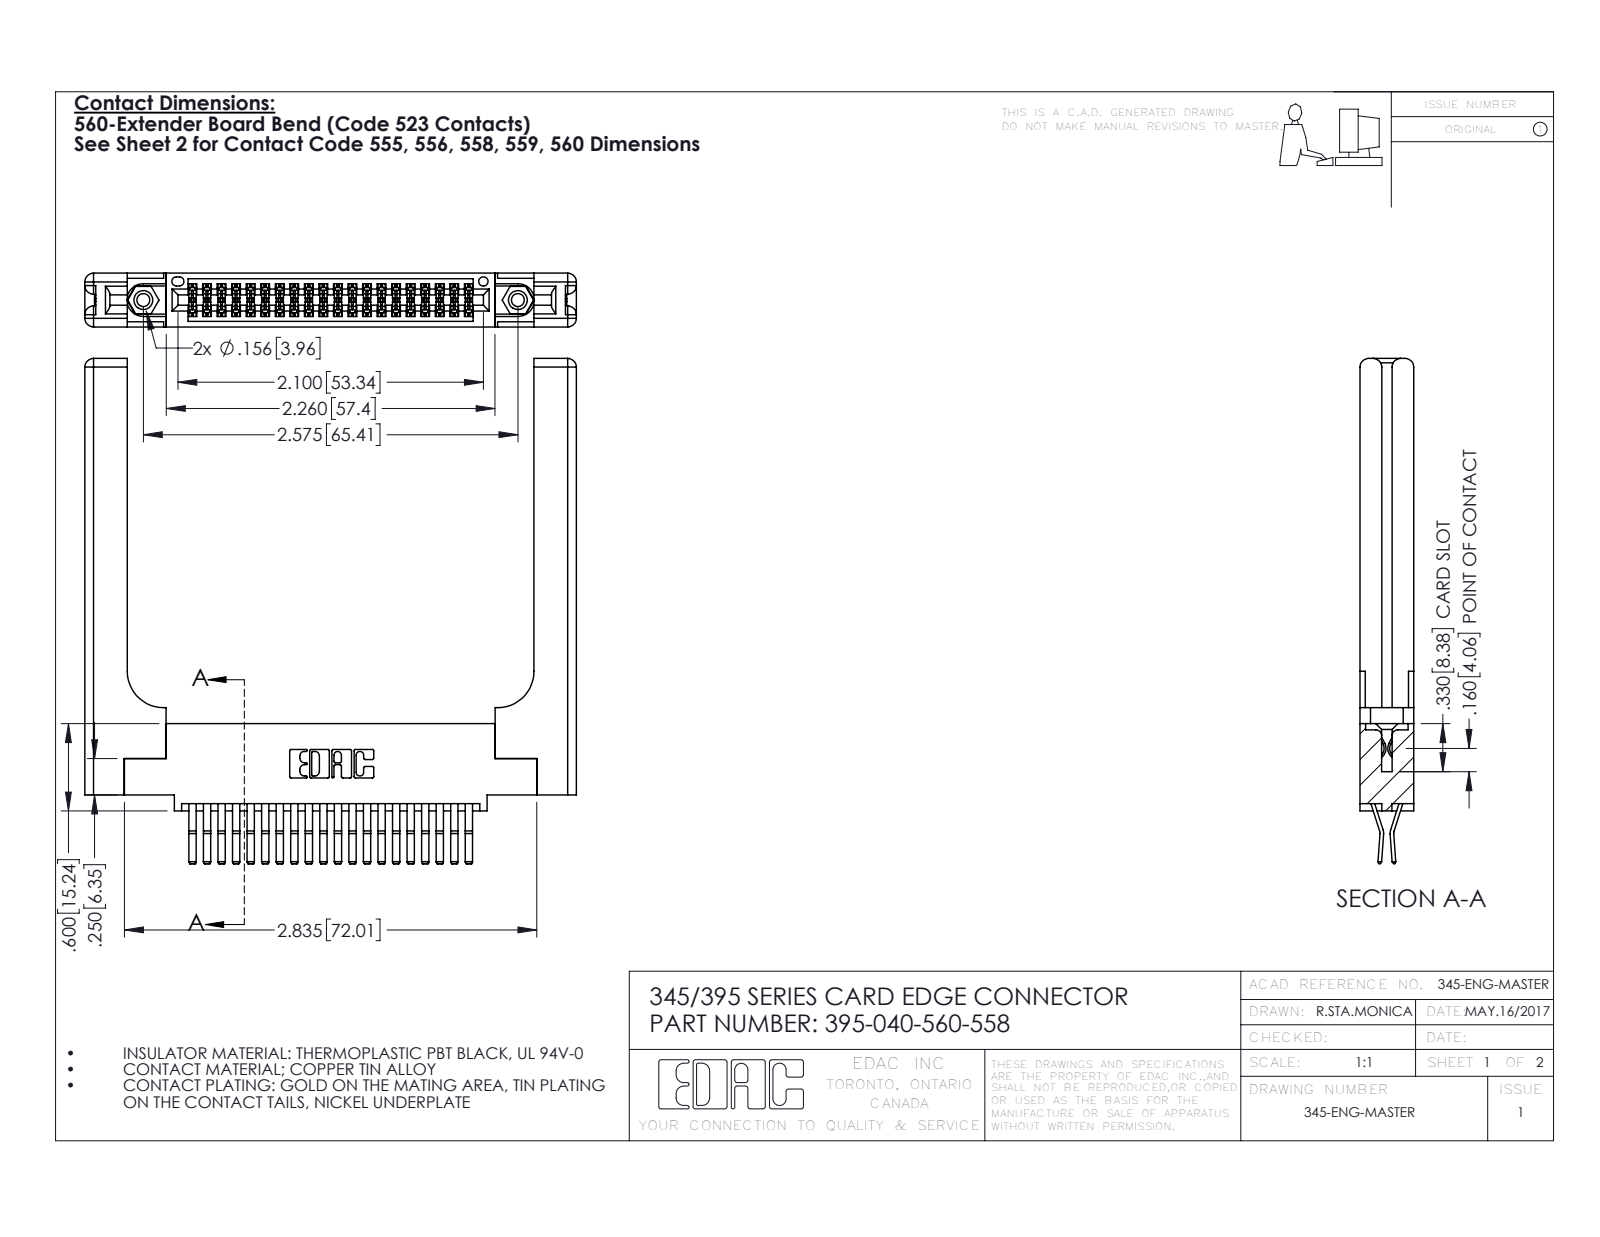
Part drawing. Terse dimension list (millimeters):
name: 395-040-560-558; 345-250-001_345-250-001-102; 345-292-001_560 Tail; 345 Part_0.110 Offset - 0.156 Dia-TH (+1 more)
written by: SolidWorks 2016 (CONFIG_CONTROL_DESIGN)
unit: mm
bodies: 45 solids, 2466 faces (1552 planar, 854 cylindrical, 60 other)
size: 88.2 × 85.8 × 9.4
volume: 16 800 mm³; area: 17 700 mm²
holes: 2× ⌀2.3, 2× ⌀3.2, 2× ⌀4, 1× ⌀1.6
bosses: 2× ⌀3.9
rounds: 60× R0.2, 22× R0.3, 16× R1.5, 6× R0.2, 6× R0.8, 3× R0.7, 2× R0.3, 2× R0.4
face distances: 9.4, 1.8, 7.6, 0.6, 3.8, 3.8, 2, 5.6, 5.7, 2.5
hole spacings: 6.9, 59.5, 65.4
